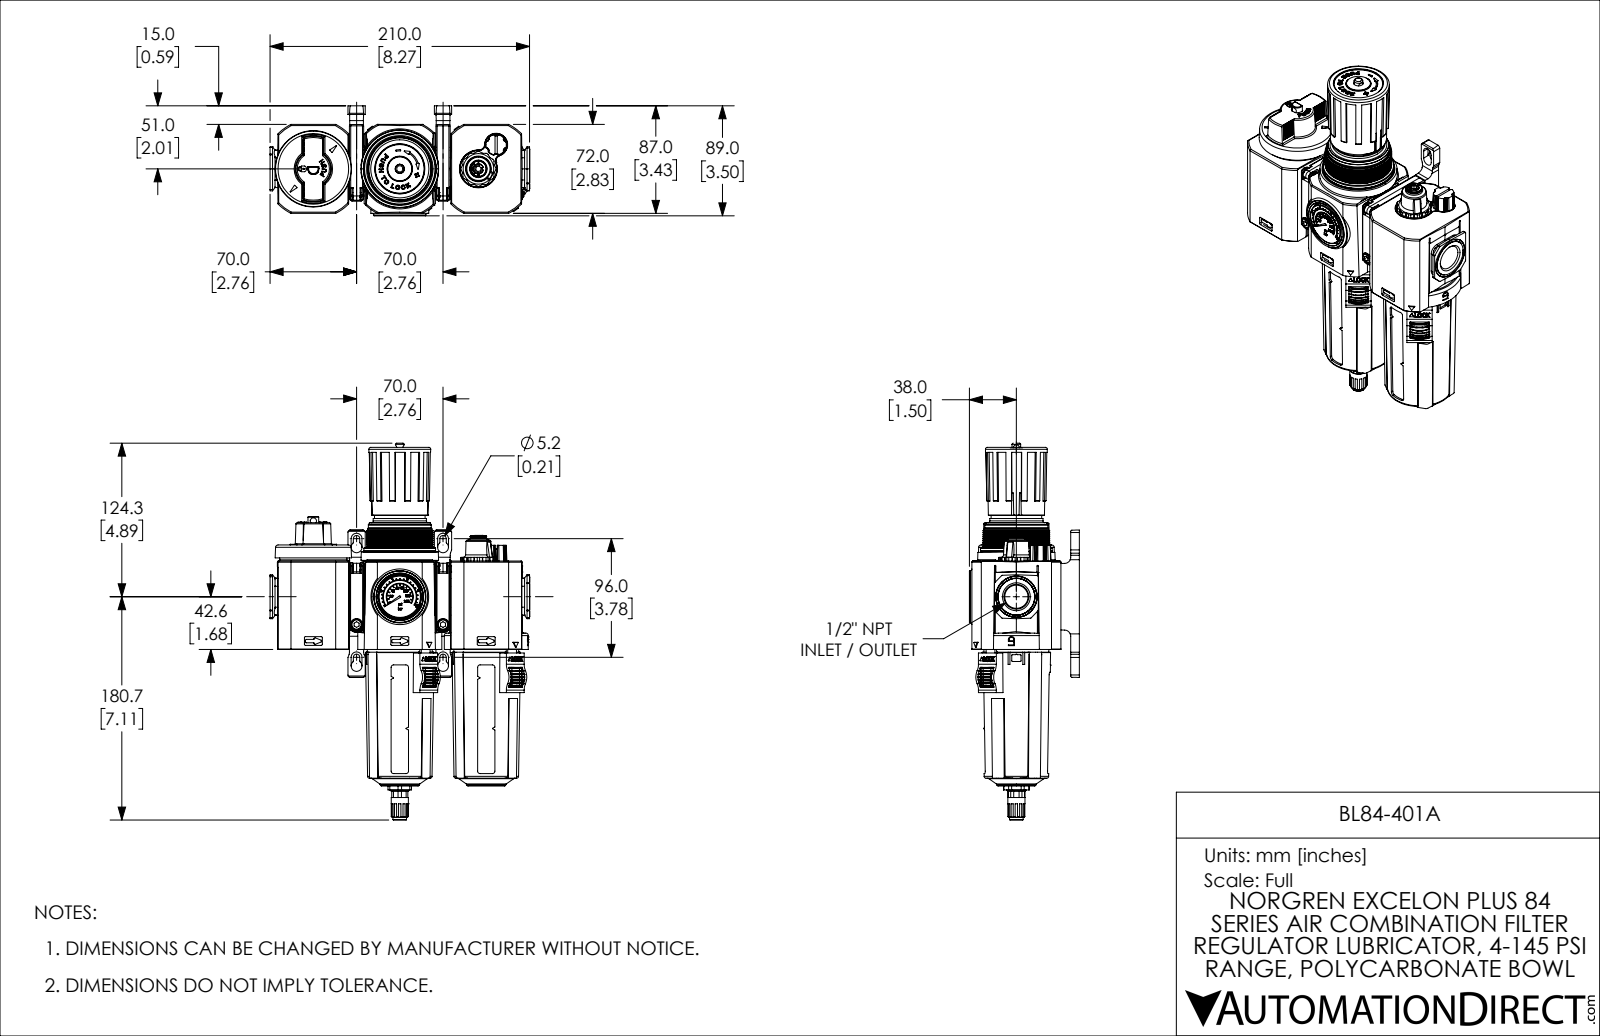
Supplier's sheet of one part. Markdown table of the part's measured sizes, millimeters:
| quantity | value |
| --- | --- |
| part name | BL84-401A |
| STEP written by | SolidWorks 2021 (CONFIG_CONTROL_DESIGN) |
| units | millimeters |
| bodies | 18 solids, 5076 faces (2136 planar, 2078 cylindrical, 862 other) |
| overall size | 304.9 × 210.3 × 89 |
| volume | 1 494 000 mm³ |
| surface area | 343 500 mm² |
| round holes (diameter × count) | 5.6 × 3, 4.1 × 2, 4.5 × 2, 5 × 2, 8.5 × 2, 24.6 × 2, 62.5 × 2, 1 × 1, 1.5 × 1, 3.2 × 1, 6.2 × 1, 6.8 × 1 |
| round bosses / shafts (diameter × count) | 5 × 4, 10 × 2, 8.5 × 2, 8.3 × 2, 7.6 × 2, 4 × 2, 58 × 1, 53.8 × 1 |
| partial cylindrical surfaces (radius × count) | 1 × 110, 0.8 × 74, 0.5 × 65, 0.3 × 51, 2 × 44, 0.7 × 32, 0.1 × 30, 0.3 × 27 |
| main face-to-face distances | 70, 140, 72, 10.3, 61.2, 74, 5.7, 71.5, 1.5, 60.4 |
| hole center spacings | 70, 4, 13.3, 21.7, 22.5, 26.1, 35, 41.6 |
